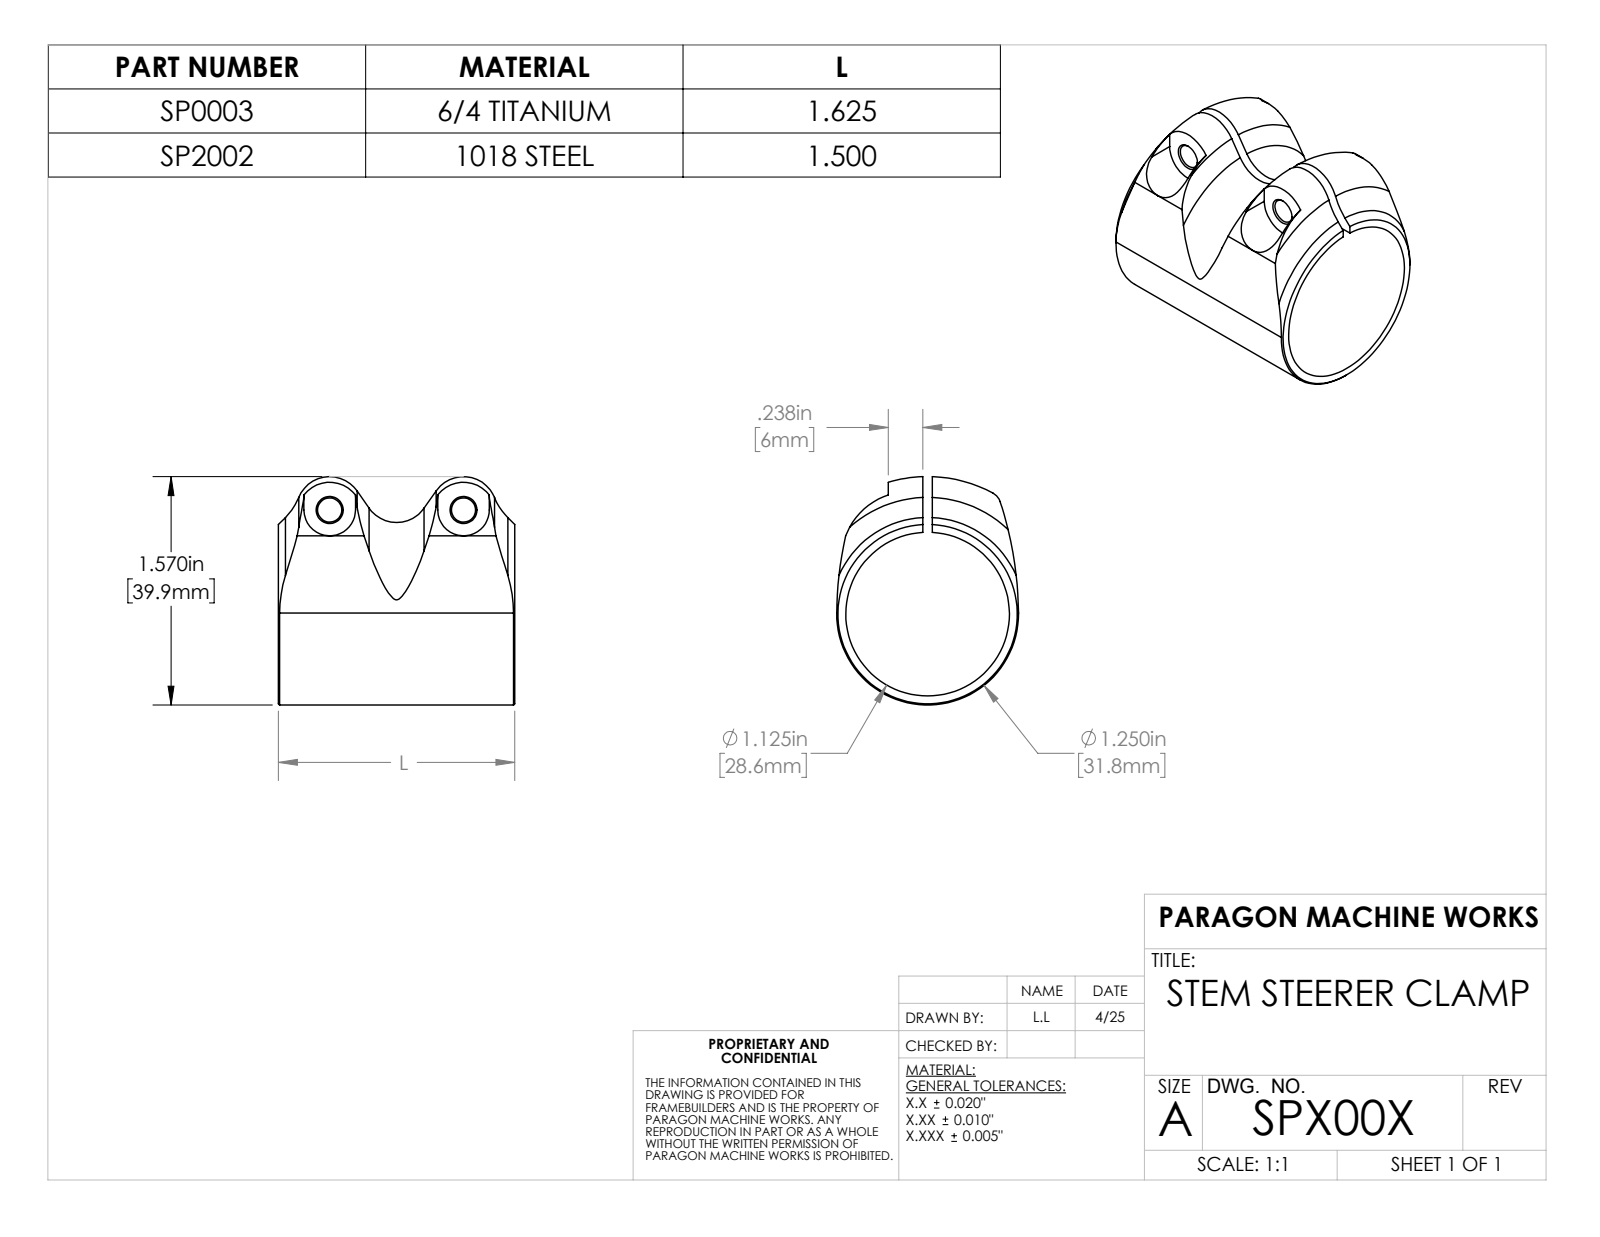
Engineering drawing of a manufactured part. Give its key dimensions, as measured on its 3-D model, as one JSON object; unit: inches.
{"part_name": "SPX00X", "step_written_by": "SolidWorks 2023 (AUTOMOTIVE_DESIGN)", "units": "inches", "bodies": {"solids": 1, "faces": 64, "planar": 10, "cylindrical": 24, "other": 30}, "overall_size": [1.625, 1.57, 1.25], "volume_in3": 0.67, "surface_area_in2": 15.22, "round_holes": [[0.166, 2], [1.125, 1]], "partial_cylinders_radius": [[0.177, 2], [2.554, 2], [0.1, 1], [0.472, 1], [0.625, 1]], "face_to_face_distances": [0.065, 1.625, 0.303, 0.237, 0.176, 0.53, 1.095, 1.45, 0.92, 0.354], "hole_center_spacings": [0.92]}
